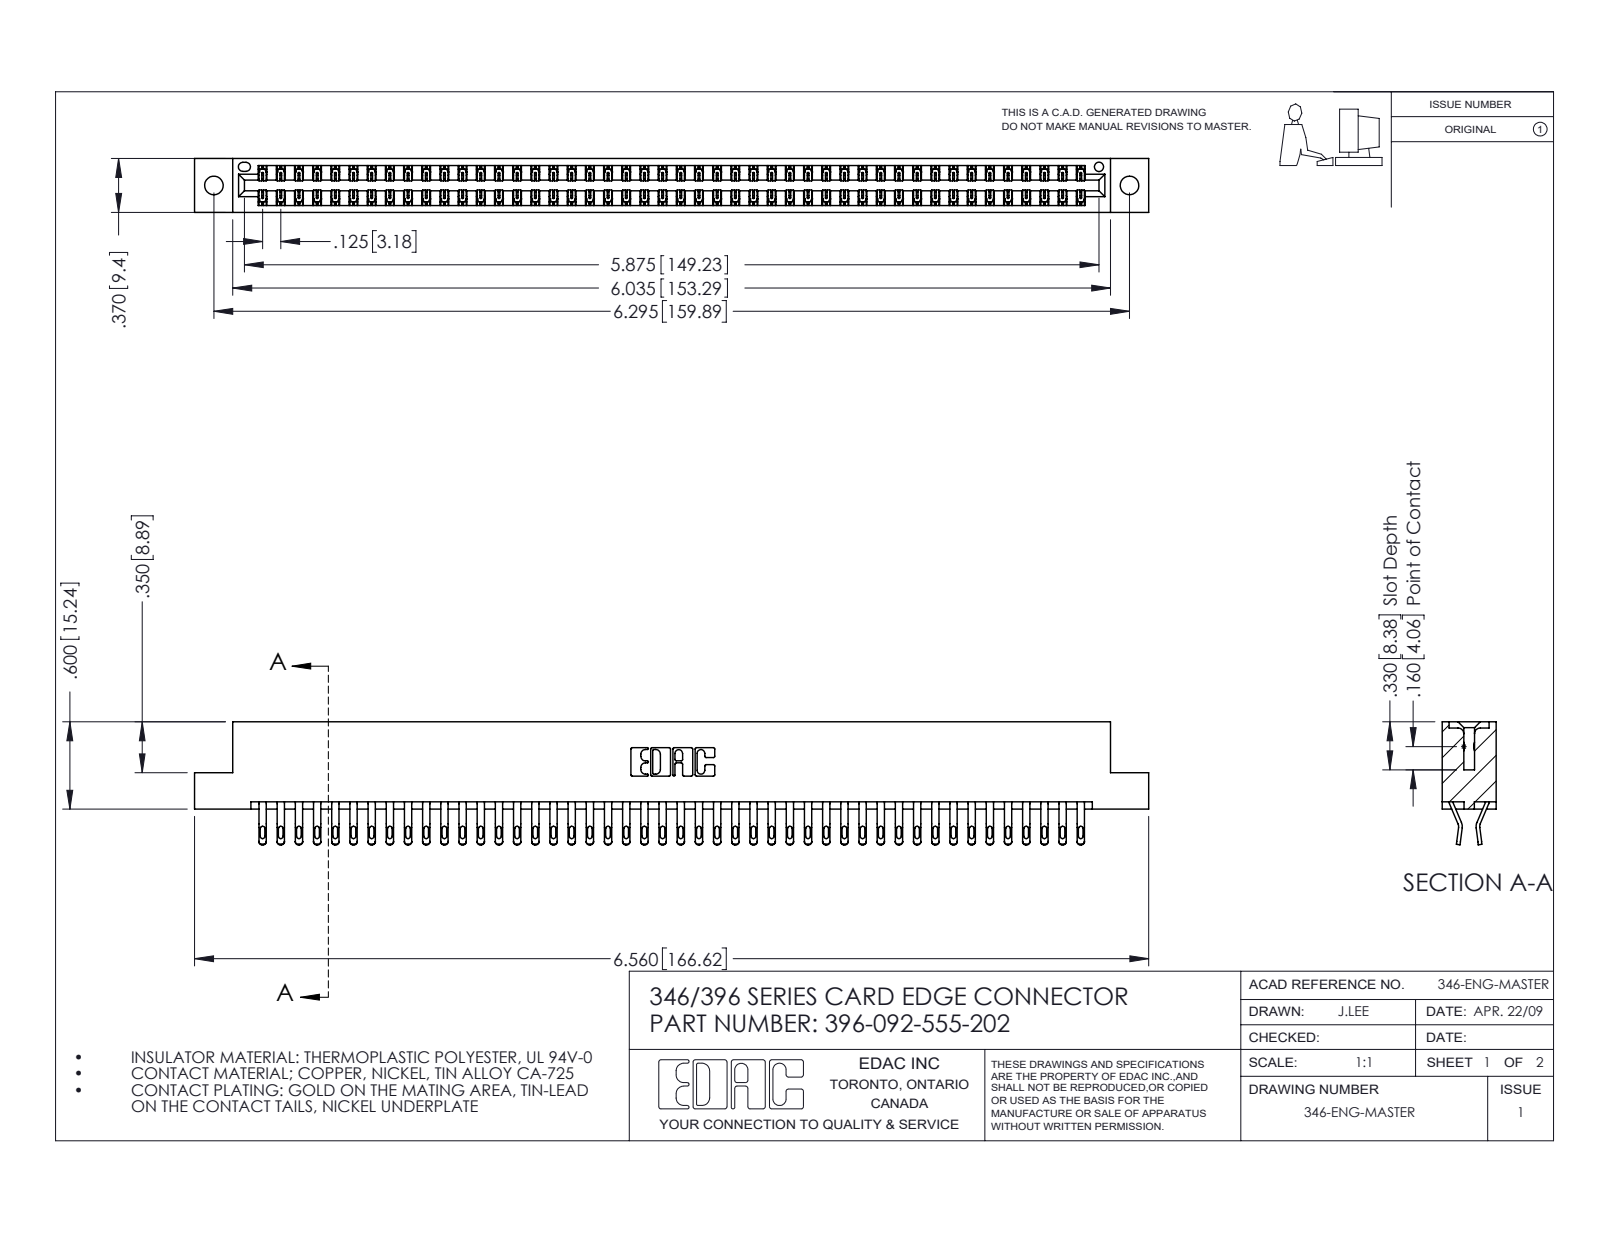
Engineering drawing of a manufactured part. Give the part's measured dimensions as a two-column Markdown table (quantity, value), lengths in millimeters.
| quantity | value |
| --- | --- |
| part name | 346 Part_Flush Mounting Lugs - 0.128 Dia; 345-292-001_555 Tail; 396-092-555-202 |
| STEP written by | SolidWorks 2016 (CONFIG_CONTROL_DESIGN) |
| units | millimeters |
| bodies | 93 solids, 5458 faces (3112 planar, 2346 cylindrical, 0 other) |
| overall size | 166.6 × 21.5 × 9.4 |
| volume | 16 500 mm³ |
| surface area | 23 440 mm² |
| round holes (diameter × count) | 3.3 × 2, 1.6 × 1 |
| partial cylindrical surfaces (radius × count) | 0.4 × 184, 0.5 × 184, 0.2 × 138, 0.3 × 22, 0.2 × 6, 0.8 × 6, 0.7 × 3, 0.3 × 2 |
| main face-to-face distances | 1.2, 8.2, 9.4, 6.4, 0.6, 1.8, 7.6, 7, 3.8, 5.6 |
| hole center spacings | 6.2, 154.6, 159.9 |
